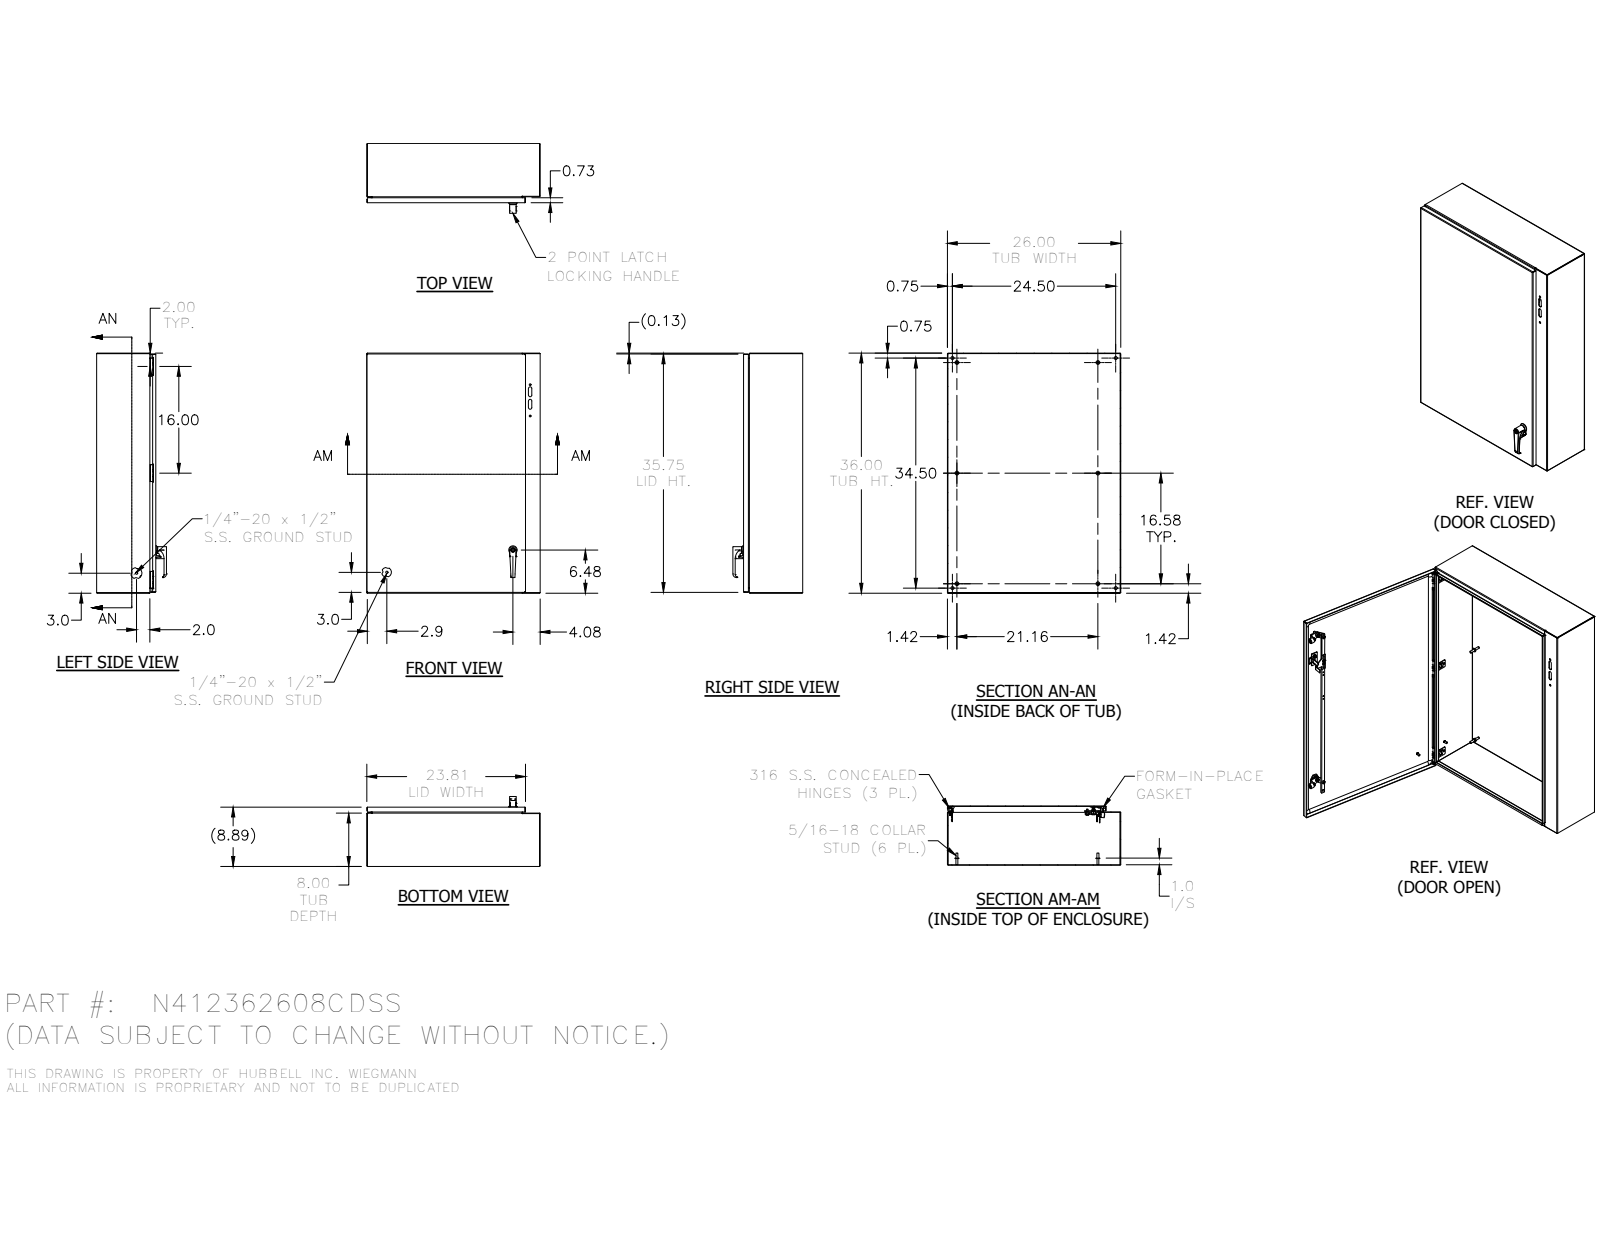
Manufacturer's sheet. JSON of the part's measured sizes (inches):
{"part_name": "N412362608CD", "step_written_by": "SolidWorks 2019 (AUTOMOTIVE_DESIGN)", "units": "inches", "bodies": {"solids": 71, "faces": 2508, "planar": 937, "cylindrical": 920, "other": 651}, "overall_size": [36, 26, 10.512], "volume_in3": 236.9, "surface_area_in2": 6345, "round_holes": [[0.093, 6], [0.145, 6], [0.152, 6], [0.167, 6], [0.172, 6], [0.187, 6], [0.156, 5], [0.437, 4], [0.32, 3], [0.196, 2], [0.211, 2], [0.22, 2]], "round_bosses_or_shafts": [[0.25, 16], [0.3, 10], [0.563, 6], [0.36, 6], [0.32, 6], [0.275, 6], [0.256, 6], [0.164, 6]], "partial_cylinders_radius": [[0.02, 38], [0.05, 38], [0.125, 33], [0.012, 30], [0.016, 26], [0.031, 18], [0.016, 16], [0.025, 16]], "face_to_face_distances": [0.074, 8.843, 8.769, 8.917, 25.926, 35.926, 0.917, 7.926, 26, 25.852], "hole_center_spacings": [16, 0.5, 32, 16.008, 0.66, 1.307, 1.965, 24.5]}
